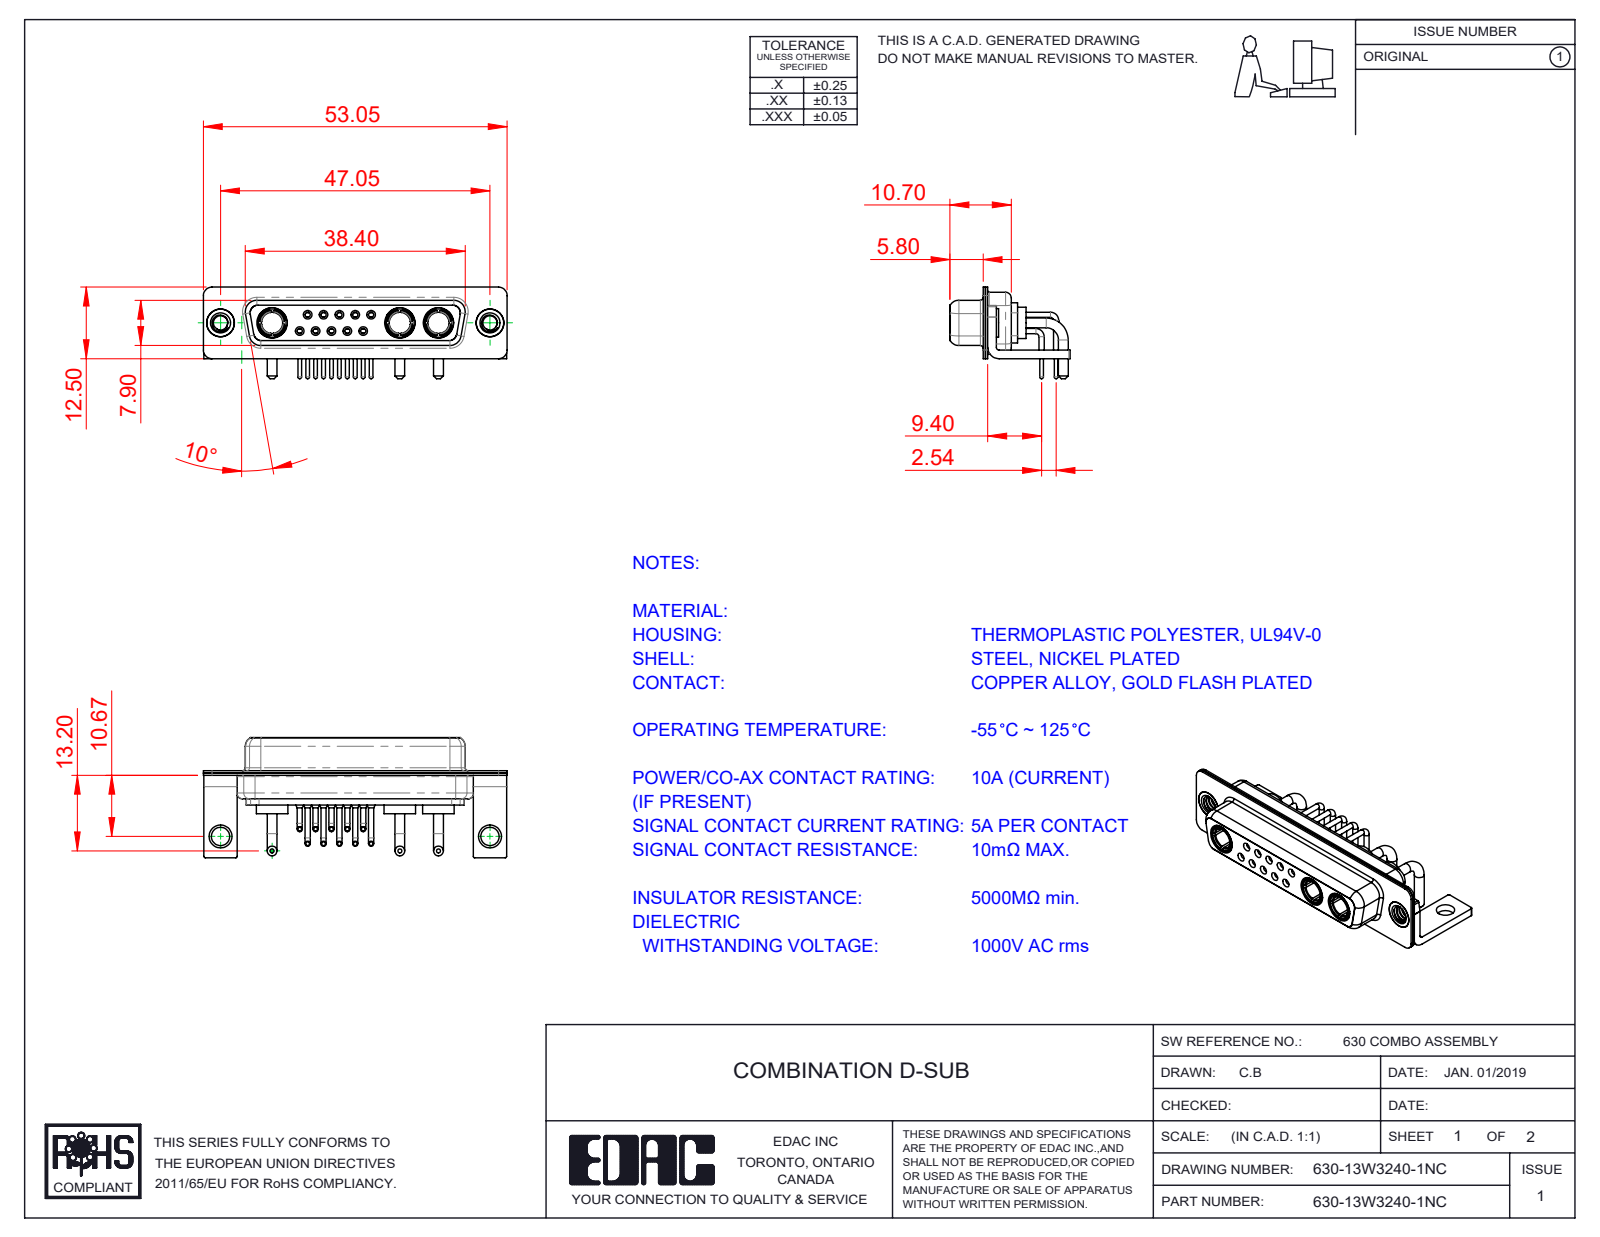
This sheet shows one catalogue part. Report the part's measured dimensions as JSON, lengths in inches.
{"part_name": "630Combo Shell Rear_25 Contacts; 630-13W3240-1NC; 630Combo Contact Row 1; 630Combo Threaded Rivet_B (+5 more)", "step_written_by": "SolidWorks 2020 (CONFIG_CONTROL_DESIGN)", "units": "inches", "bodies": {"solids": 23, "faces": 1081, "planar": 324, "cylindrical": 460, "other": 297}, "overall_size": [2.089, 0.827, 0.63], "volume_in3": 0.251, "surface_area_in2": 14.66, "round_holes": [[0.035, 10], [0.043, 10], [0.059, 10], [0.079, 10], [0.063, 5], [0.067, 5], [0.191, 5], [0.146, 3], [0.209, 3], [0.098, 2], [0.126, 2], [0.157, 2]], "round_bosses_or_shafts": [[0.035, 10], [0.026, 10], [0.067, 6], [0.063, 5], [0.217, 3], [0.205, 3], [0.195, 3], [0.187, 3]], "partial_cylinders_radius": [[0.01, 16], [0.059, 16], [0.079, 13], [0.053, 8], [0.063, 8], [0.02, 5], [0.024, 4], [0.026, 4]], "face_to_face_distances": [0.016, 0.018, 0.055, 0.333, 0.071, 0.35, 0.031, 0.059, 0.244, 0.278], "hole_center_spacings": [0.124, 0.109, 0.218, 0.198, 0.198, 0.327, 0.294, 0.295]}
